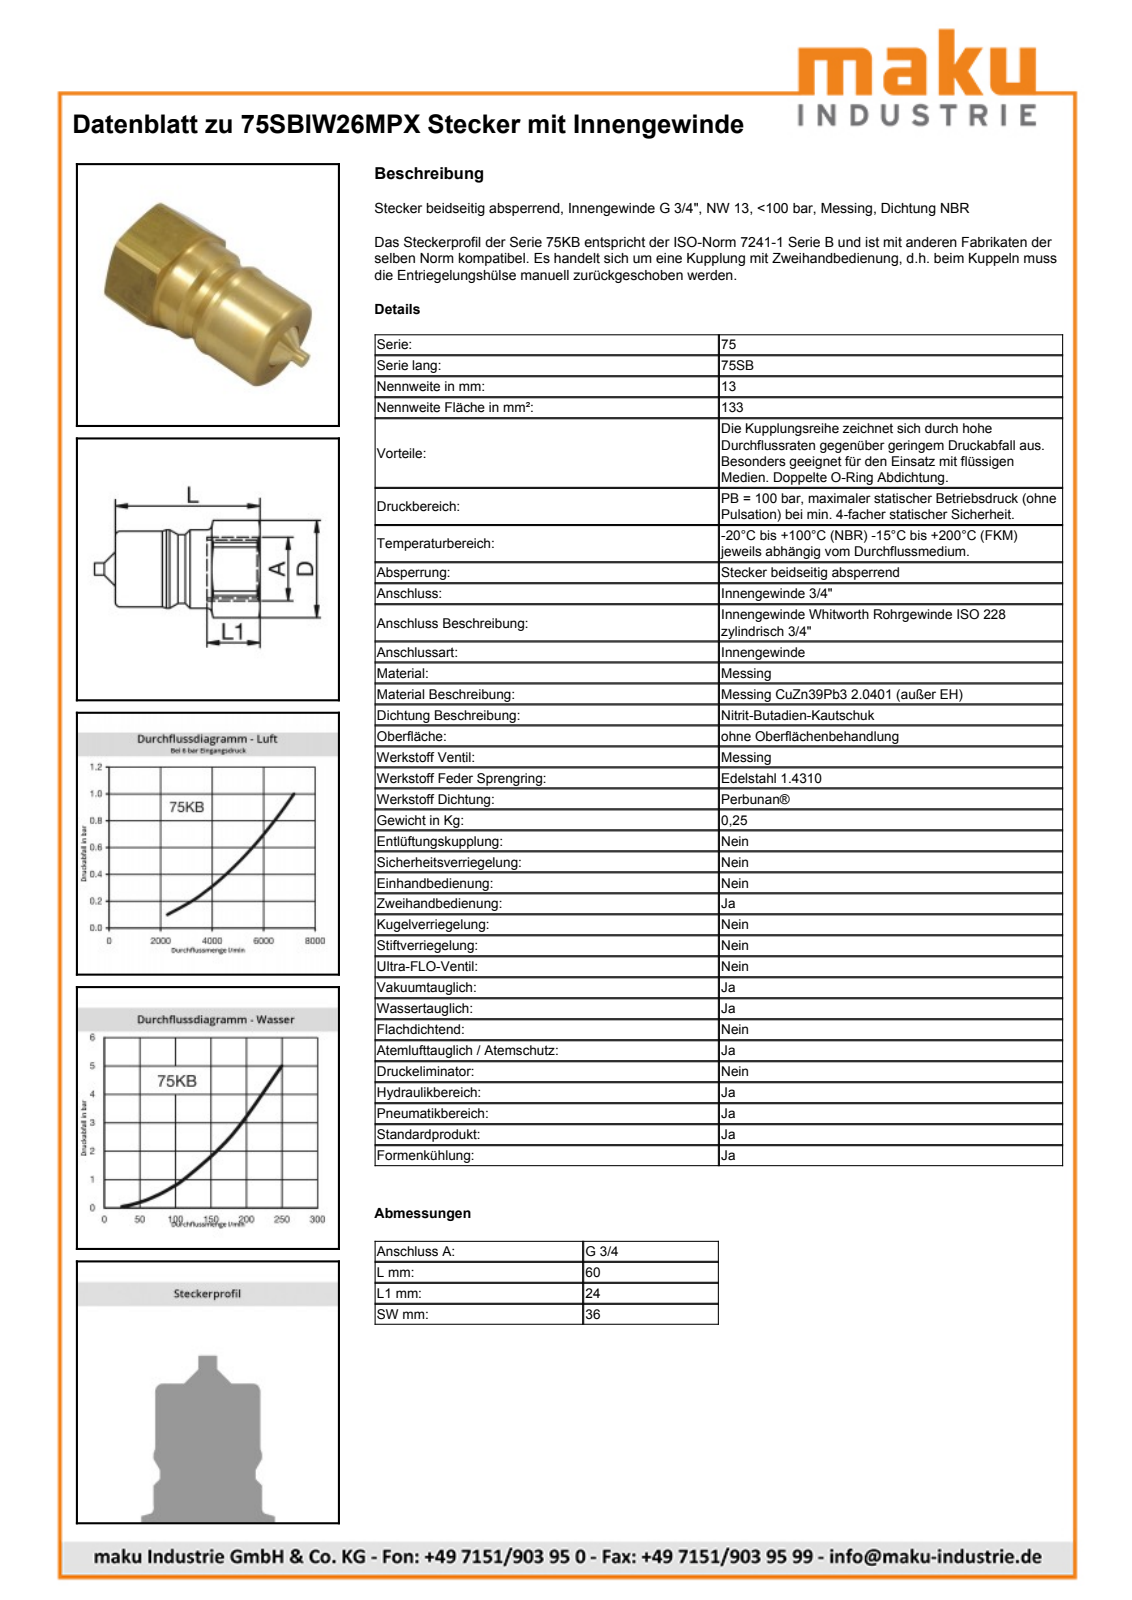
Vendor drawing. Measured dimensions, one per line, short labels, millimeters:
name: D107368
written by: Autodesk Inventor 2013 (AUTOMOTIVE_DESIGN)
unit: mm
bodies: 1 solid, 70 faces (26 planar, 19 cylindrical, 25 other)
size: 68.6 × 40.35 × 36
volume: 41 149 mm³; area: 12 298 mm²
holes: 1× ⌀15.2, 1× ⌀17, 1× ⌀24, 1× ⌀24.12
bosses: 1× ⌀32.5, 1× ⌀31.4, 1× ⌀28.5, 1× ⌀16.8, 1× ⌀10.7, 1× ⌀10, 1× ⌀5
rounds: 1× R20.18
face distances: 36, 22, 38, 60, 12.63, 25.37, 47.37, 5.4, 7.23, 32.6
